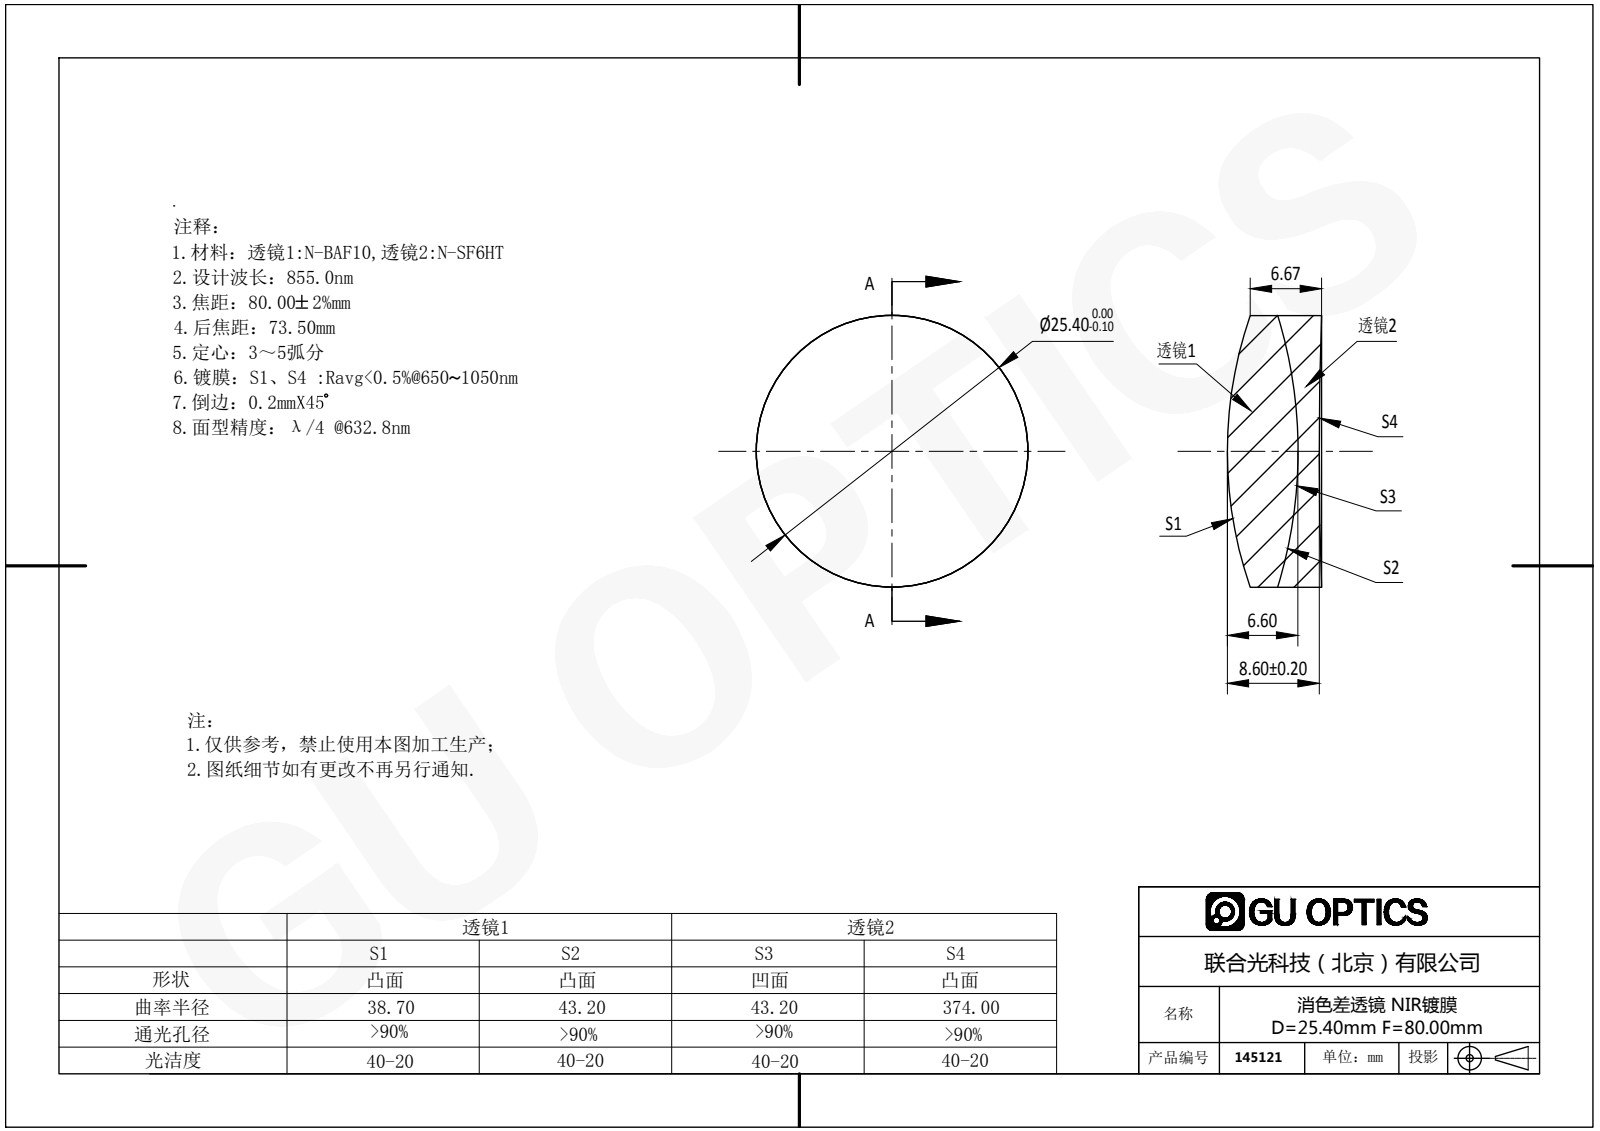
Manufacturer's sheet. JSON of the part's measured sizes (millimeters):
{"part_name": "145121", "step_written_by": "SolidWorks 2016 (AUTOMOTIVE_DESIGN)", "units": "millimeters", "bodies": {"solids": 2, "faces": 12, "planar": 0, "cylindrical": 4, "other": 8}, "overall_size": [25.4, 25.4, 8.82], "volume_mm3": 3874, "surface_area_mm2": 2597, "round_bosses_or_shafts": [[25.4, 1]]}
